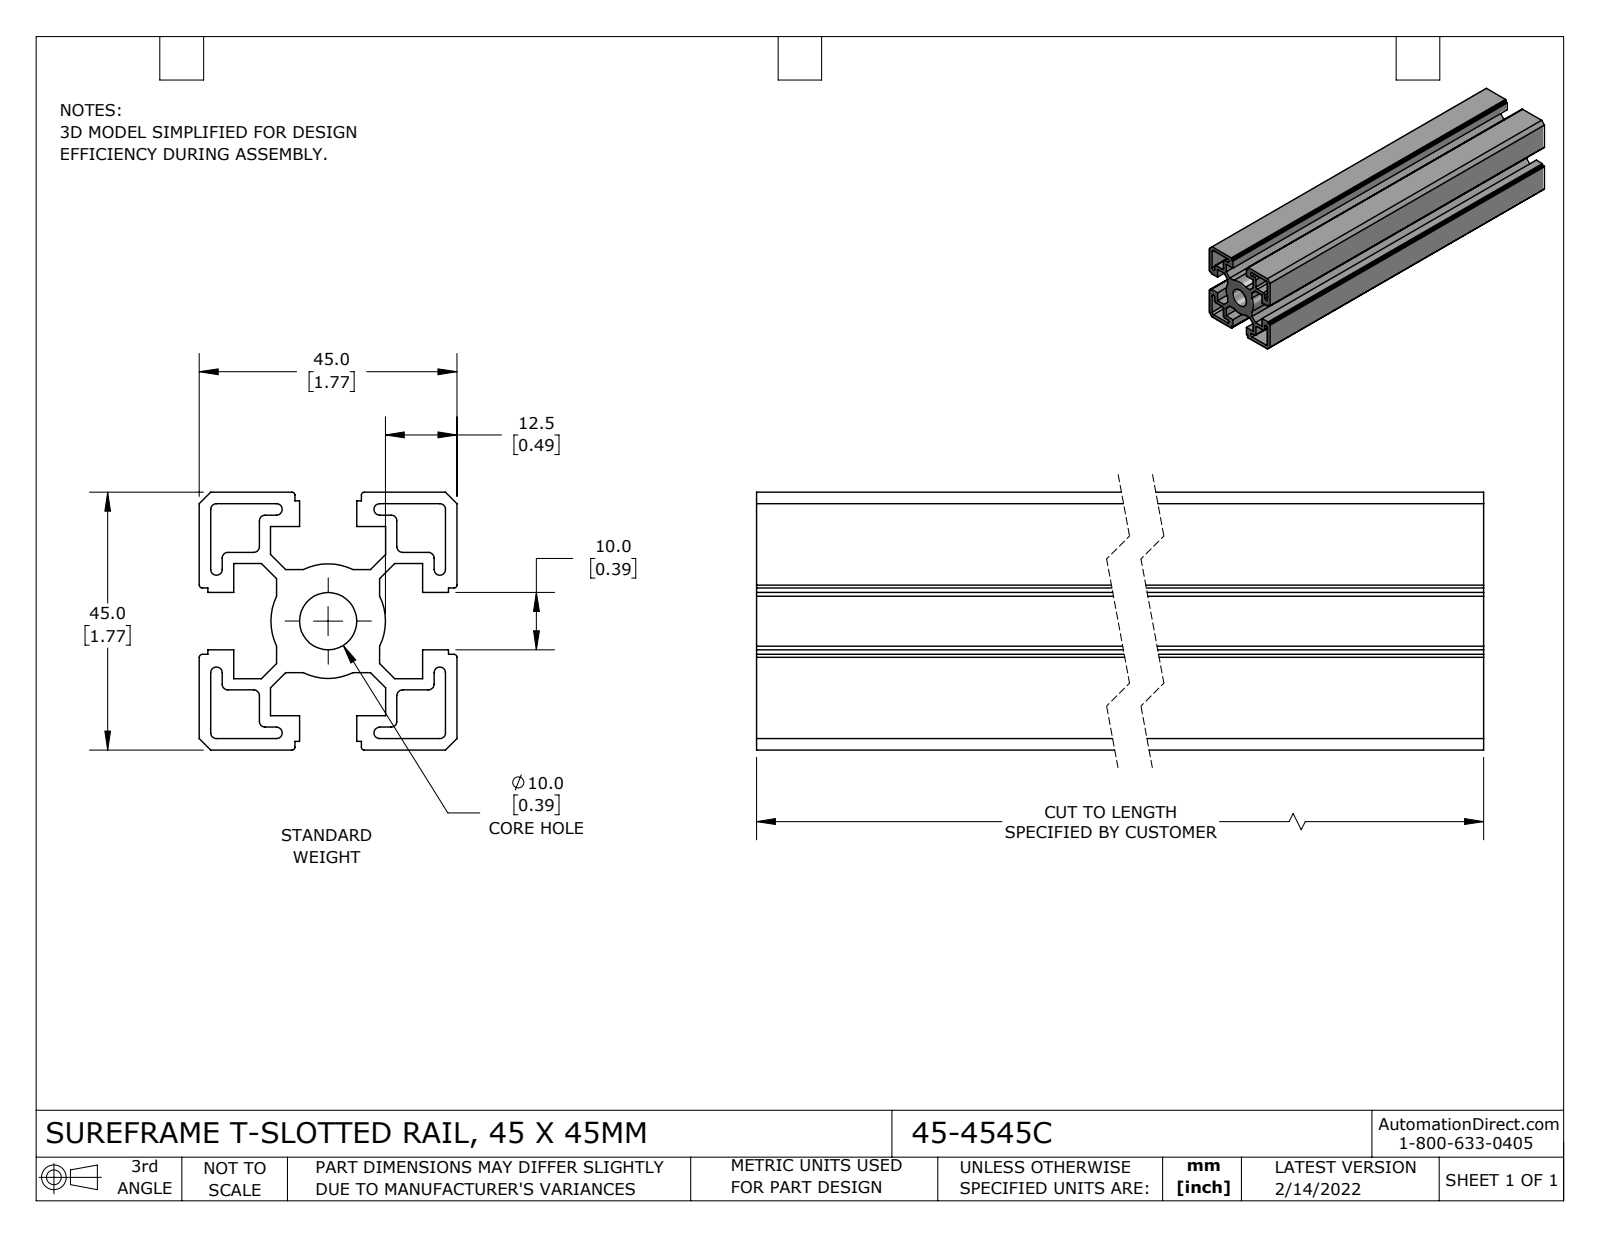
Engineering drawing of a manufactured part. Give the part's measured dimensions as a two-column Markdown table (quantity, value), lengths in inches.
| quantity | value |
| --- | --- |
| part name | 45-4545C |
| STEP written by | SolidWorks 2021 (CONFIG_CONTROL_DESIGN) |
| units | inches |
| bodies | 1 solid, 134 faces (94 planar, 40 cylindrical, 0 other) |
| overall size | 8 × 1.772 × 1.772 |
| volume | 9.761 in³ |
| surface area | 181.6 in² |
| round holes (diameter × count) | 0.394 × 1 |
| partial cylindrical surfaces (radius × count) | 0.039 × 24, 0.02 × 8, 0.394 × 1 |
| main face-to-face distances | 0.079, 1.693, 0.157, 0.453, 1.004, 1.614, 1.772, 1.535, 1.083, 1.457 |
